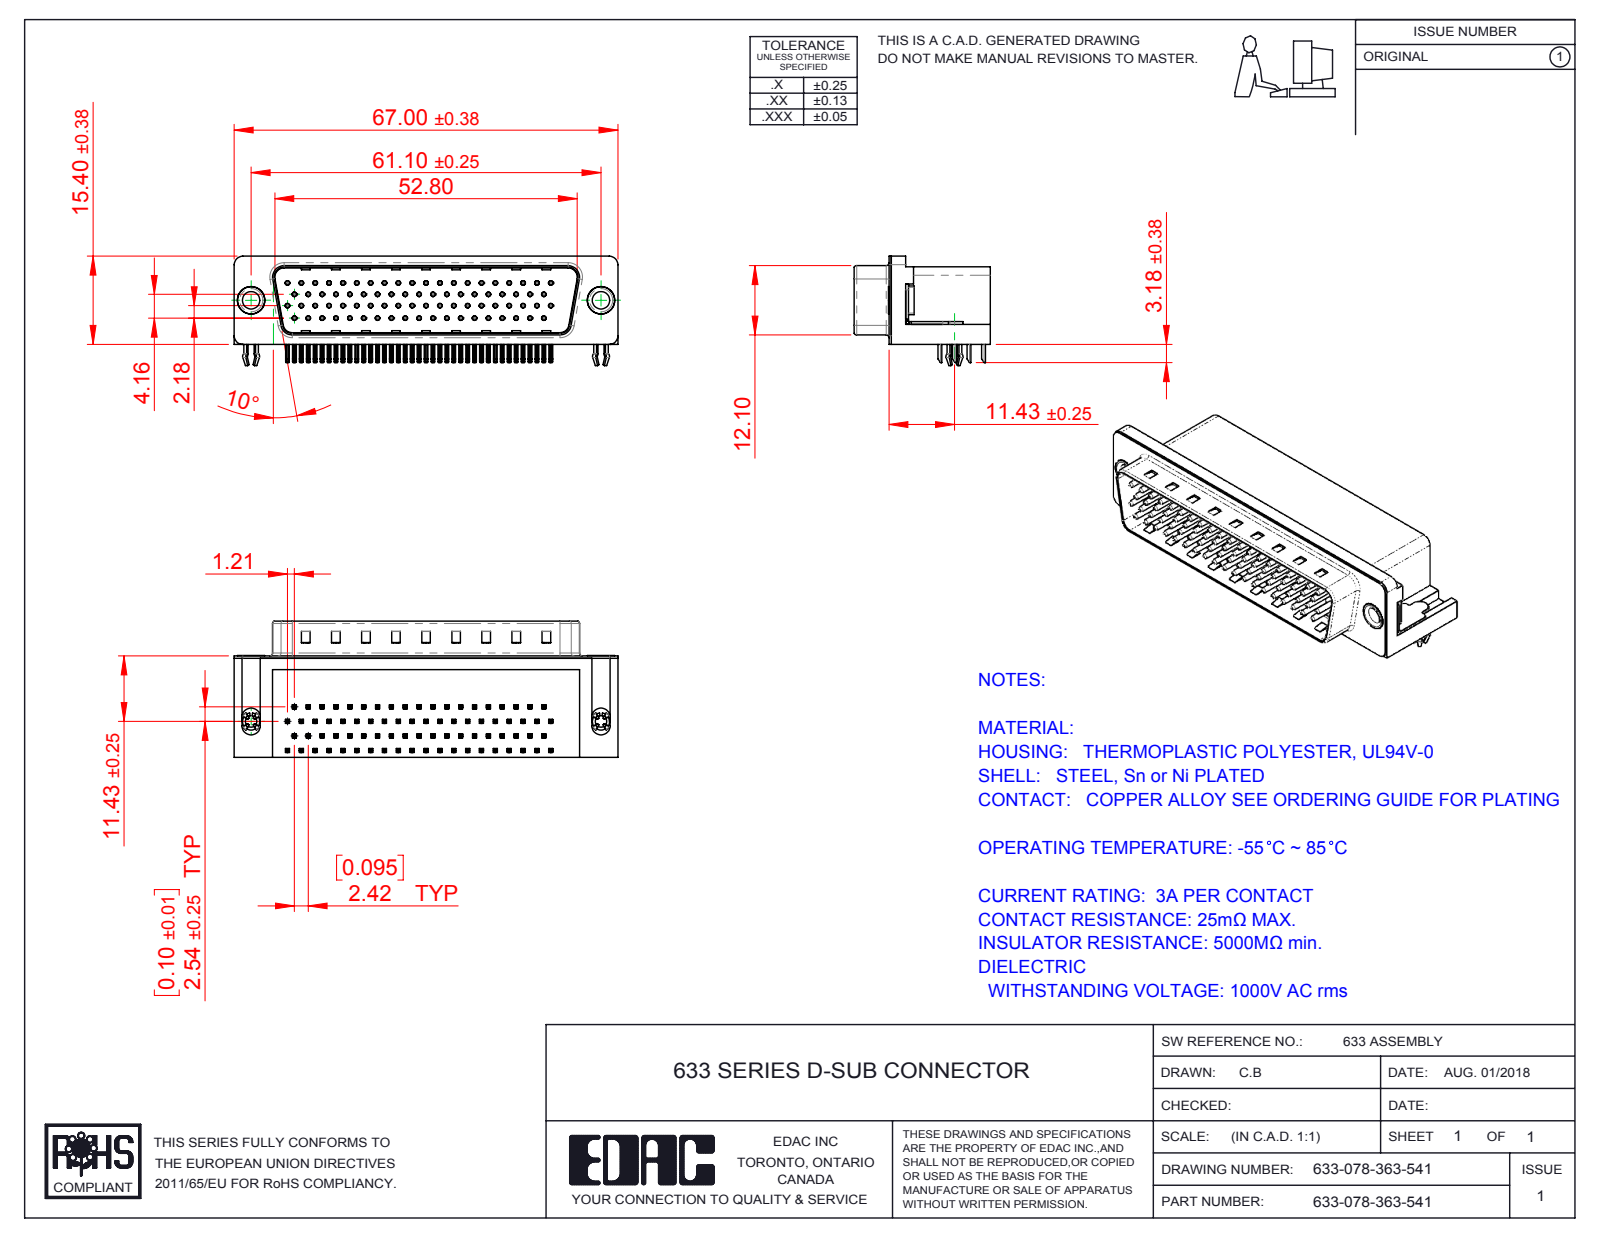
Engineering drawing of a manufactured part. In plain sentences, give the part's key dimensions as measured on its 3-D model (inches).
The part is named "633 4 Prong Board Lock_78 Contact; 633 Contact Top 78; 633 Contact Top_78 Contact; 633 Contact Middle_78 Contact (+5 more)". Its 3-D file was written by "SolidWorks 2016 (CONFIG_CONTROL_DESIGN)". It is 84 solids with 6356 faces: 4023 planar, 1766 cylindrical and 567 other. Overall it measures 2.638 by 0.937 by 0.752 inches. Its volume is 0.892 cubic inches and its surface area 25.44 square inches. Round holes: 78 of diameter 0.014, 78 of diameter 0.031, 2 of diameter 0.079, 2 of diameter 0.12, 2 of diameter 0.157, 2 of diameter 0.189, 2 of diameter 0.197. Round bosses or shafts: 78 of diameter 0.03, 2 of diameter 0.193, 2 of diameter 0.187, 2 of diameter 0.152, 2 of diameter 0.118. Partial cylindrical surfaces (rounded edges, fillets, slot ends): 324 of radius 0.01, 156 of radius 0.005, 16 of radius 0.039, 9 of radius 0.02, 8 of radius 0.063, 6 of radius 0.059, 4 of radius 0.018, 4 of radius 0.035. The main face-to-face distances are 0.016, 0.52, 0.681, 0.461, 0.526, 0.081, 0.541, 0.065, 0.073, 0.469. The hole center spacings are 0.095, 0.191, 0.286, 0.381, 0.246, 0.281, 0.476, 0.339.
